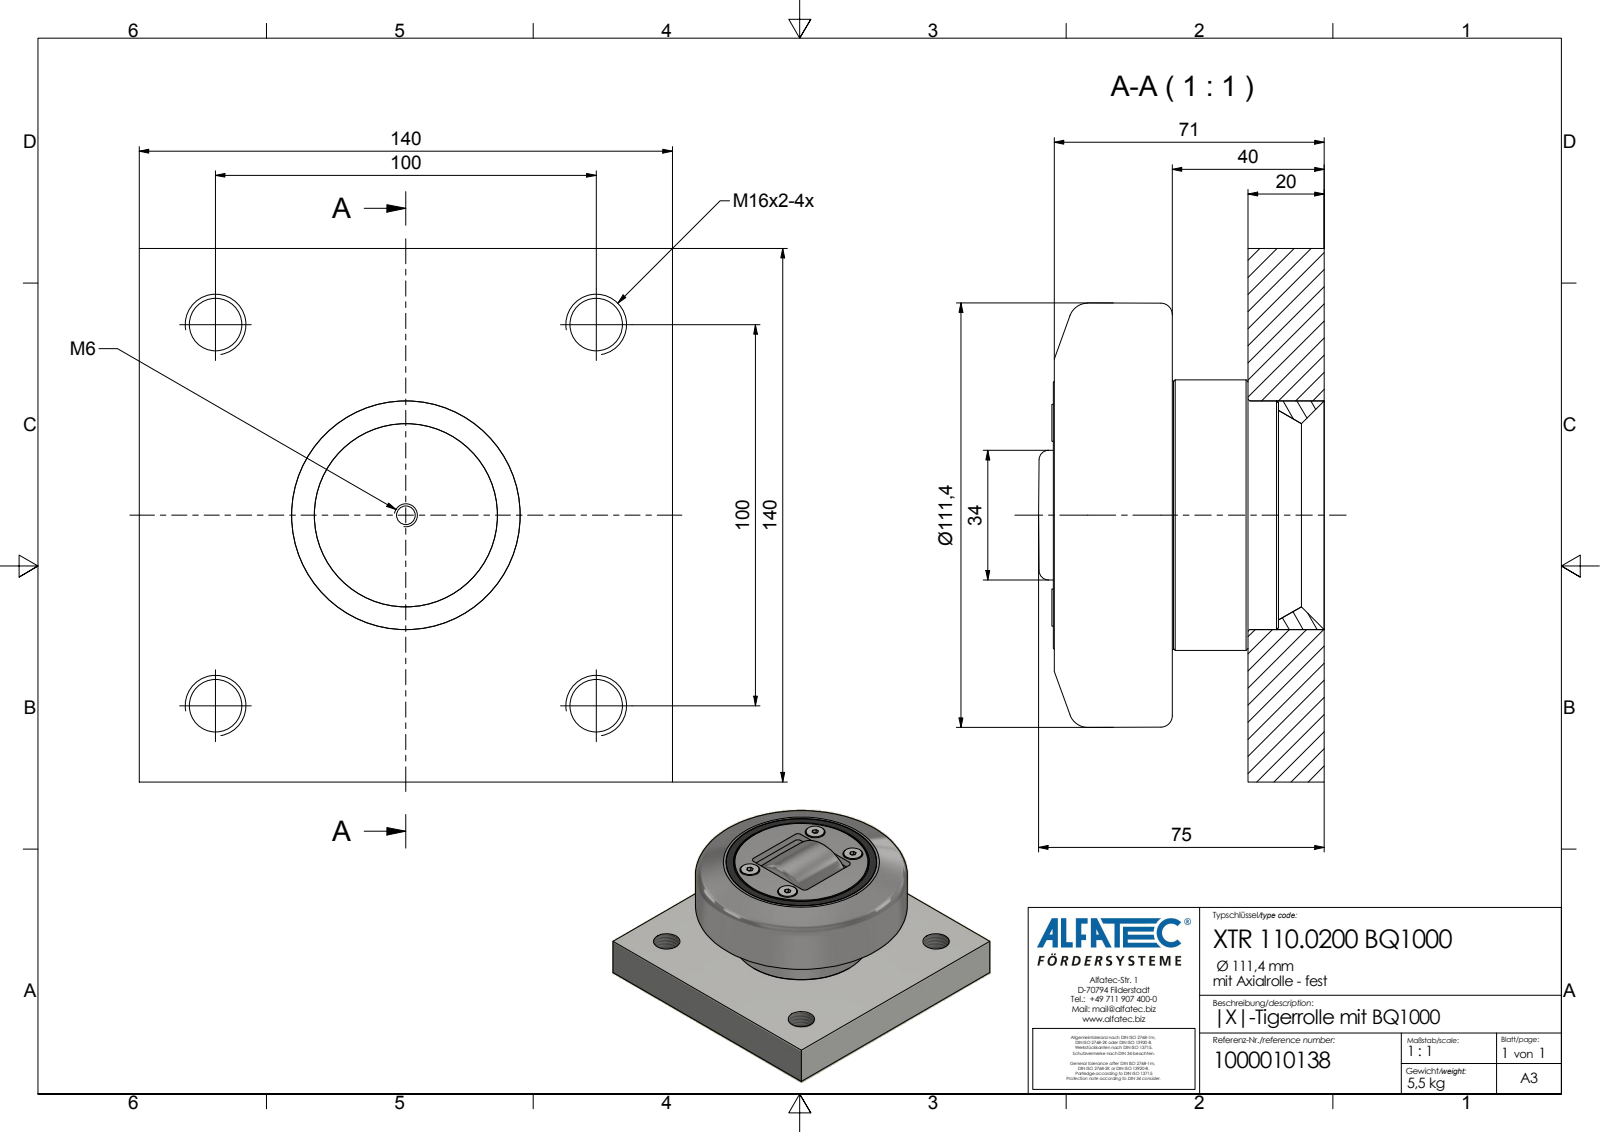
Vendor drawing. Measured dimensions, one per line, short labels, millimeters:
name: XTR 110.0200 BQ1000_Kontur
written by: Autodesk Inventor 2020 (AUTOMOTIVE_DESIGN)
unit: mm
bodies: 3 solids, 175 faces (74 planar, 58 cylindrical, 43 other)
size: 140 × 140 × 75
volume: 676 507 mm³; area: 119 315 mm²
holes: 4× ⌀3, 4× ⌀5.5, 4× ⌀13.84, 1× ⌀4.92, 1× ⌀20.1, 1× ⌀26, 1× ⌀30, 1× ⌀62.9, 1× ⌀63, 1× ⌀71.5, 1× ⌀78, 1× ⌀79
bosses: 4× ⌀9.75, 4× ⌀5, 1× ⌀77, 1× ⌀75, 1× ⌀71, 1× ⌀70.5, 1× ⌀69.3, 1× ⌀61.5
rounds: 8× R2, 2× R1.5, 1× R22
face distances: 20, 140, 39.9, 19.9, 4, 6.5, 6, 71.1, 51.1, 31.2
hole spacings: 28, 44.26, 68.99, 70.71, 82.52, 98.03, 100, 48.5
